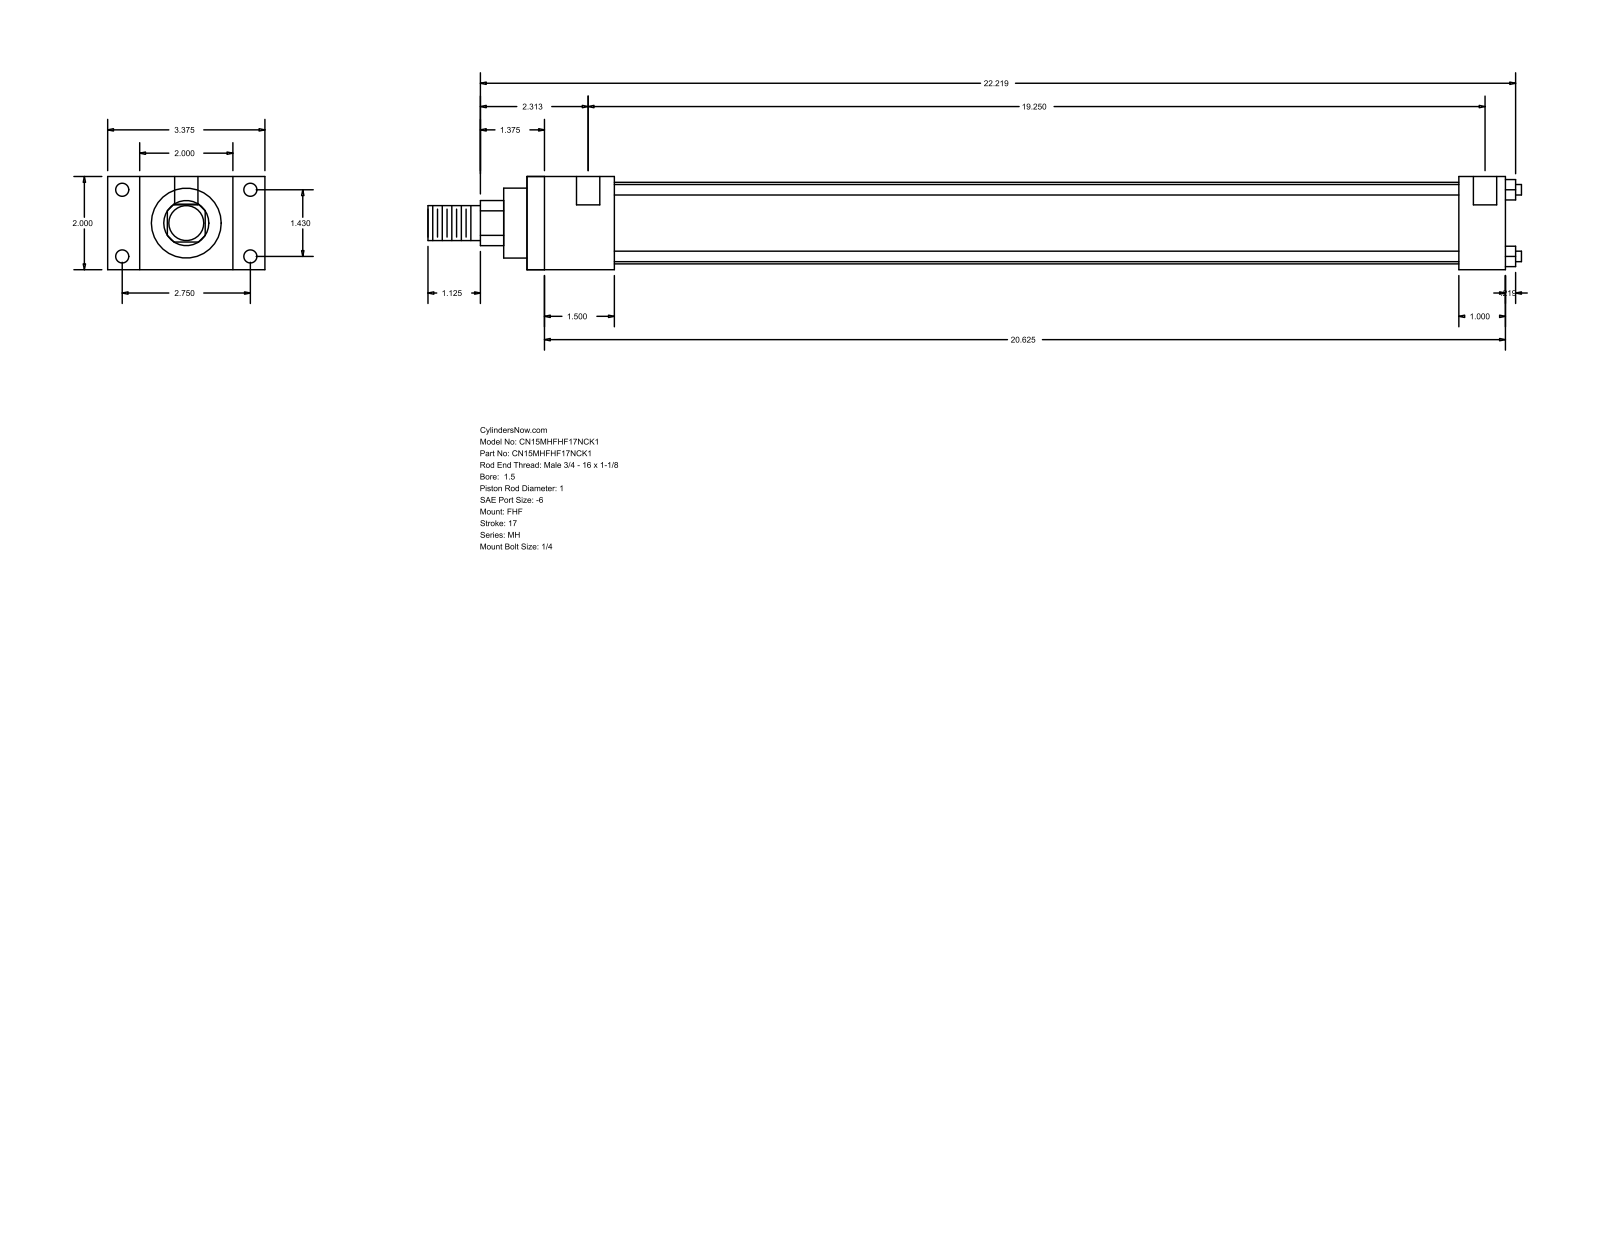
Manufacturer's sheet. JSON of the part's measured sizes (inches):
{"part_name": "MH_FHF__0150_1", "step_written_by": "GSSL Pune (CONFIG_CONTROL_DESIGN)", "units": "inches", "bodies": {"solids": 0, "faces": 88, "planar": 60, "cylindrical": 28, "other": 0}, "overall_size": [23.469, 3.375, 2], "round_holes": [[0.219, 4], [0.281, 4], [0.5, 2]], "round_bosses_or_shafts": [[0.225, 4], [1.75, 1], [1.5, 1], [1, 1], [0.75, 1]], "partial_cylinders_radius": [[0.484, 1]], "face_to_face_distances": [2, 0.687, 2.687, 1.875, 3.375, 21, 19.125, 1, 20, 18.125], "hole_center_spacings": [1.43, 2.75, 3.099, 19.375, 0.125, 19.25]}
